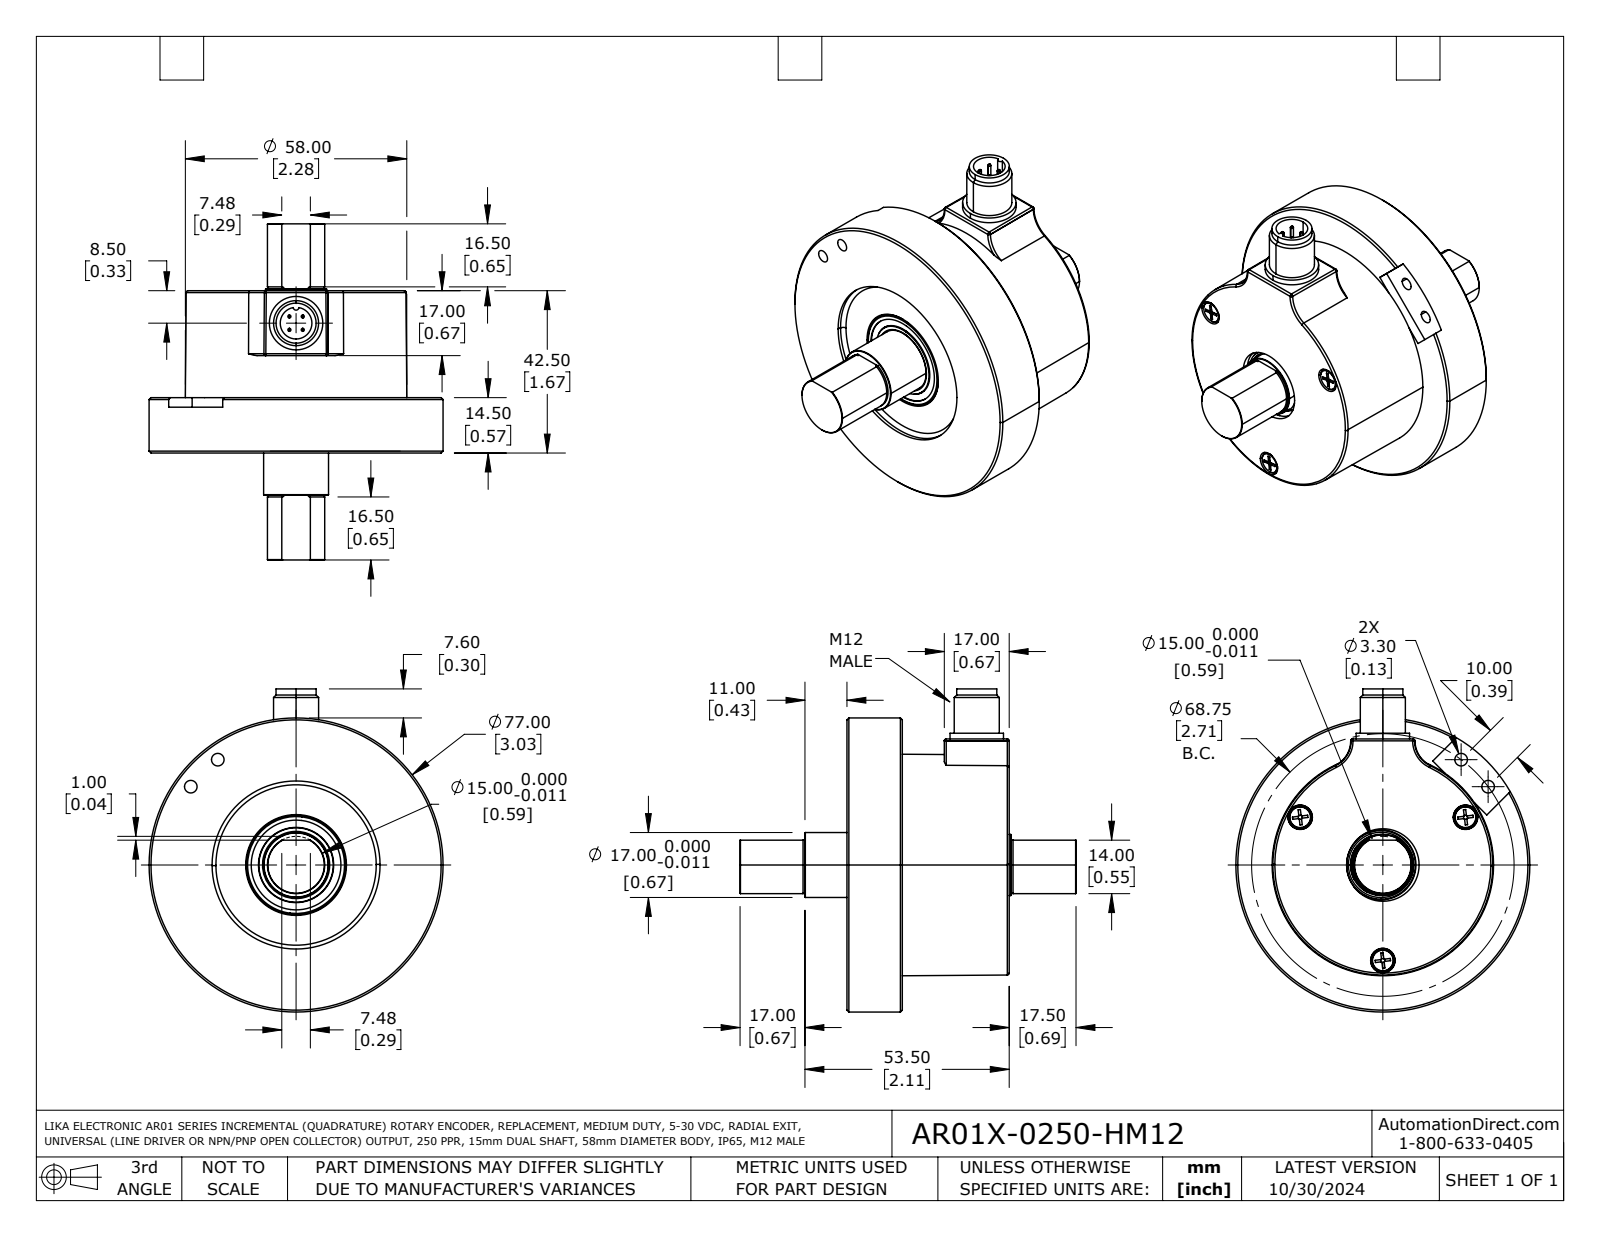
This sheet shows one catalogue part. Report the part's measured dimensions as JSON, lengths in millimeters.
{"part_name": "AR01X-0250-HM12", "step_written_by": "SolidWorks 2021 (AUTOMOTIVE_DESIGN)", "units": "millimeters", "bodies": {"solids": 10, "faces": 1346, "planar": 838, "cylindrical": 204, "other": 304}, "overall_size": [88, 84.6, 77], "volume_mm3": 92420, "surface_area_mm2": 41820, "round_holes": [[2.5, 6], [3.3, 2], [8, 1], [8.3, 1], [10, 1], [10.5, 1], [19, 1], [19.7, 1], [23.3, 1], [23.5, 1], [23.5, 1], [24, 1]], "round_bosses_or_shafts": [[1.4, 4], [0.8, 4], [3, 3], [77, 1], [56, 1], [53.5, 1], [24, 1], [23, 1]], "partial_cylinders_radius": [[0.2, 9], [0.5, 9], [0.2, 3], [0.8, 3], [2, 1], [6, 1]], "face_to_face_distances": [42.5, 28, 14.5, 3, 17.5, 25, 26.5, 23.5, 1.5, 15.6], "hole_center_spacings": [25, 43.3, 8.7, 34.4, 0.5, 10, 10, 10.8]}
